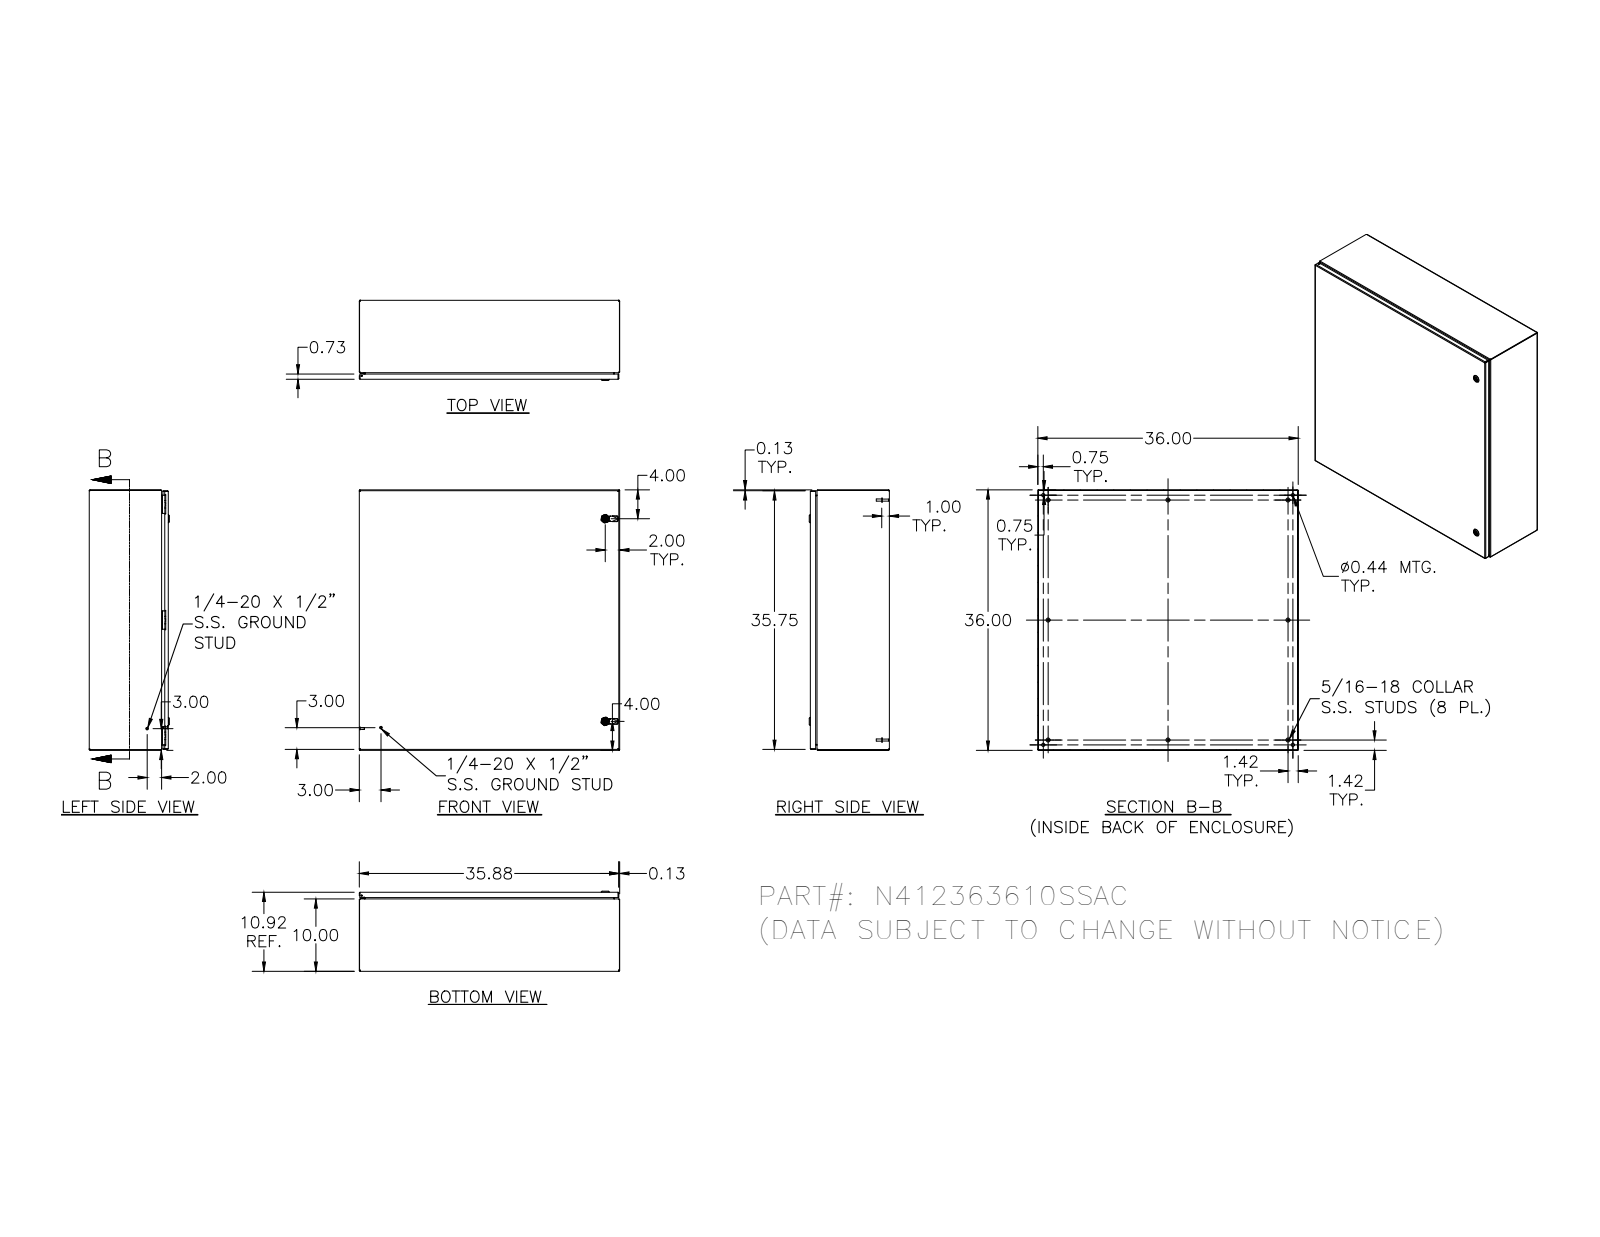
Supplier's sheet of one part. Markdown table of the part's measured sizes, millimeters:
| quantity | value |
| --- | --- |
| part name | N412SSACASSM1PC; N412363610SSACBKP; 388151; N4123636SSACLID (+8 more) |
| STEP written by | Autodesk Inventor 2012 (AUTOMOTIVE_DESIGN) |
| units | millimeters |
| bodies | 55 solids, 2132 faces (839 planar, 782 cylindrical, 511 other) |
| overall size | 914.4 × 914.4 × 281.3 |
| volume | 5 254 000 mm³ |
| surface area | 5 606 000 mm² |
| round holes (diameter × count) | 2.4 × 6, 3.9 × 6, 4.2 × 6, 4.4 × 6, 4.8 × 6, 11.1 × 4, 4 × 3, 5 × 2, 8 × 2, 10 × 2, 10.2 × 2, 16.1 × 2 |
| round bosses / shafts (diameter × count) | 6.4 × 14, 14.3 × 8, 7.6 × 8, 7 × 8, 9.1 × 6, 8.1 × 6, 6.5 × 6, 4.2 × 6 |
| partial cylindrical surfaces (radius × count) | 1.3 × 38, 0.8 × 34, 0.4 × 26, 3.2 × 21, 2.7 × 20, 0.5 × 15, 0.8 × 12, 1.8 × 8 |
| main face-to-face distances | 1.9, 275.4, 912.5, 273.5, 277.3, 910.6, 914.4, 252.1, 23.3, 18.8 |
| hole center spacings | 406.5, 812.8, 406.3, 0.4, 16.8, 406.2, 406.4, 406.6 |
